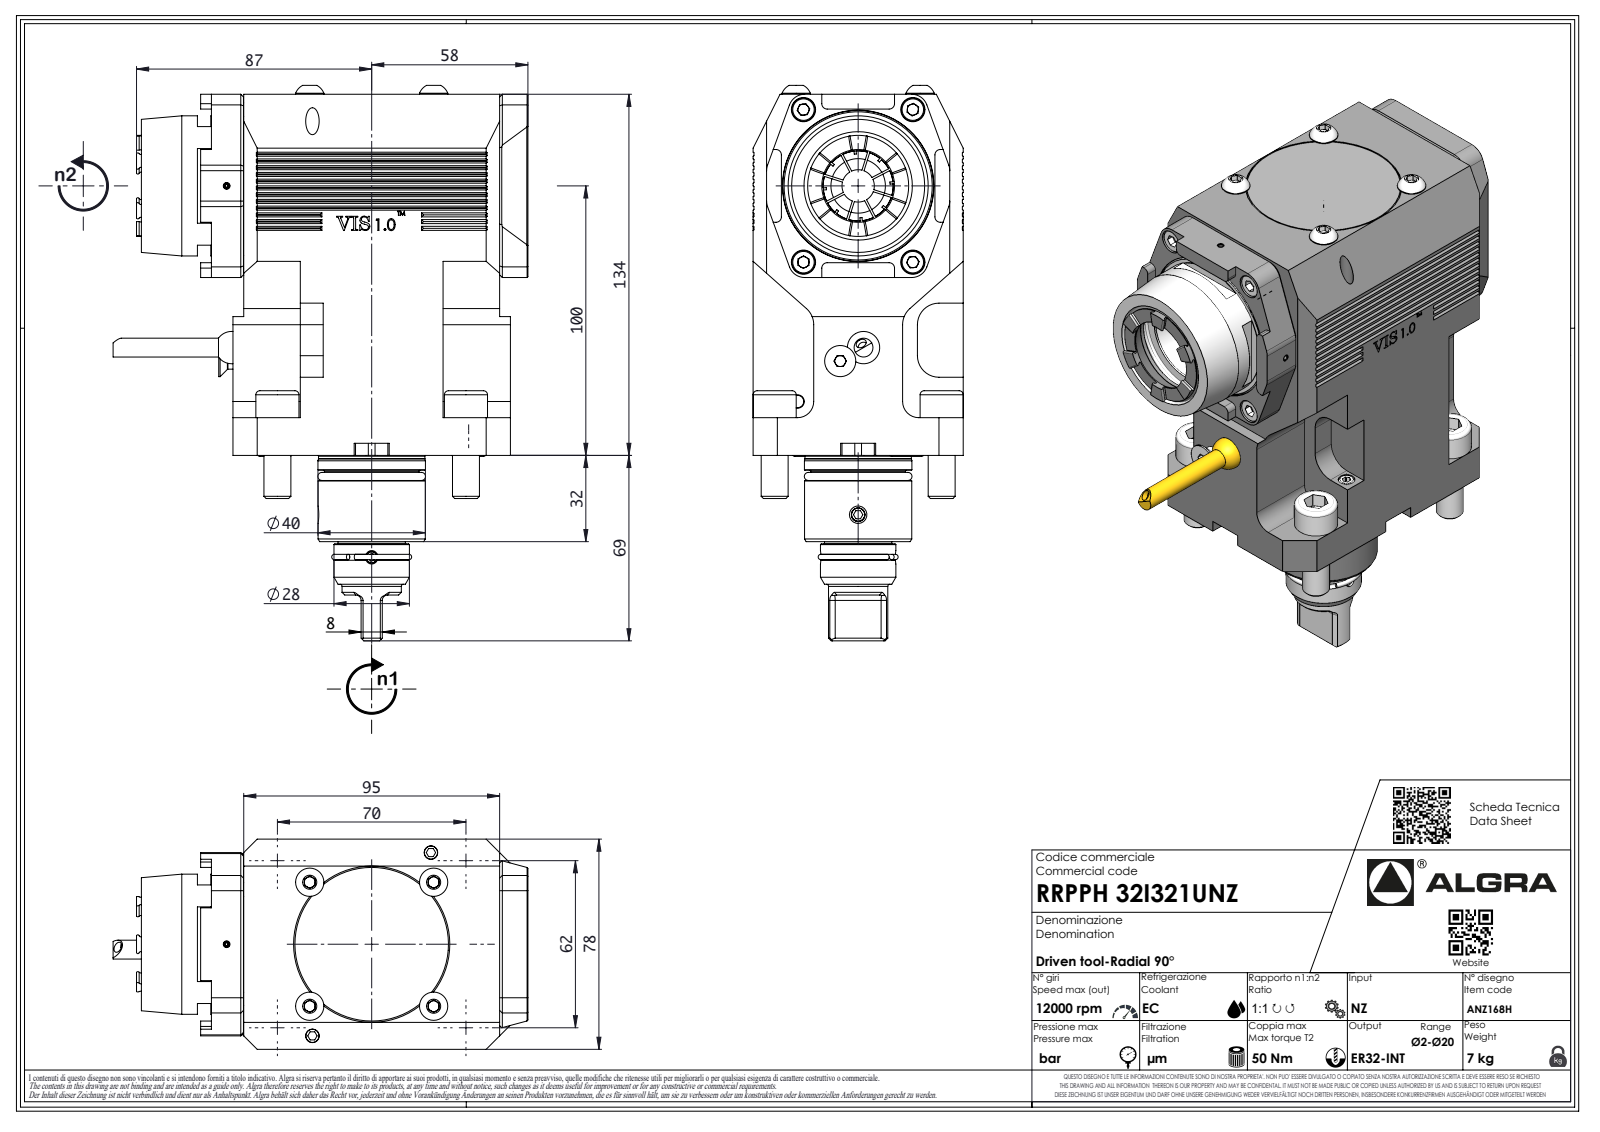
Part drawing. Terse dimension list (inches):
name: RRPPH32I321UNZ
written by: SolidWorks 2023 (AUTOMOTIVE_DESIGN)
unit: in
bodies: 1 solid, 852 faces (584 planar, 114 cylindrical, 154 other)
size: 7.984 × 6.083 × 3.071
volume: 66.94 in³; area: 145 in²
holes: 1× ⌀0.083, 1× ⌀0.157, 1× ⌀0.319
bosses: 4× ⌀0.63, 4× ⌀0.394, 1× ⌀2.047, 1× ⌀1.571, 1× ⌀1.567, 1× ⌀1.555, 1× ⌀1.382, 1× ⌀1.378
rounds: 16× R0.197, 15× R0.079, 10× R0.236, 7× R0.013, 7× R0.02, 7× R0.146, 6× R0.315, 1× R0.008
face distances: 3.071, 5.276, 0.157, 4.173, 3.898, 0.984, 2.913, 0.827, 0.886, 0.472
